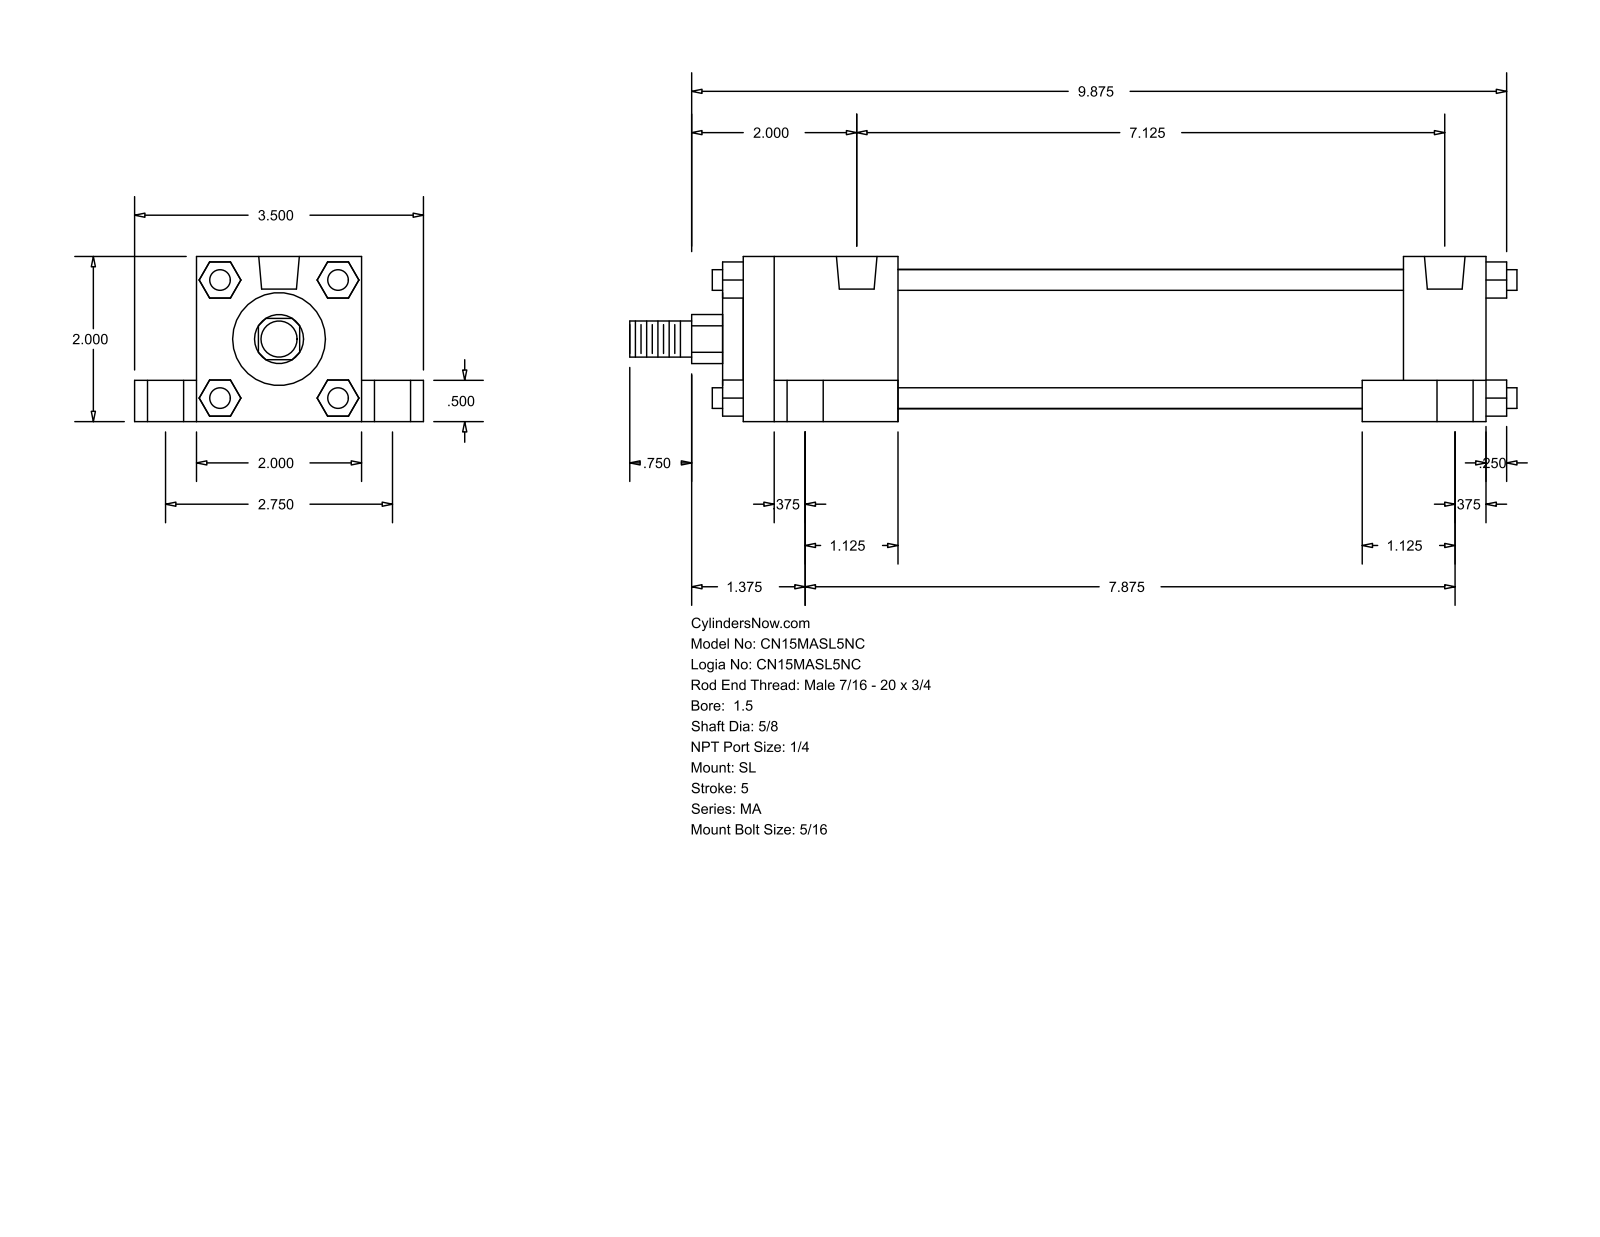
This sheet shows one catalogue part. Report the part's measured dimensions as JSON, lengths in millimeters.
{"part_name": "MA_SL__0150_0.625", "step_written_by": "GSSL Pune (CONFIG_CONTROL_DESIGN)", "units": "millimeters", "bodies": {"solids": 0, "faces": 148, "planar": 112, "cylindrical": 36, "other": 0}, "overall_size": [273.05, 88.9, 50.8], "round_holes": [[7.94, 4], [11.11, 4], [17.46, 4], [12.49, 2]], "round_bosses_or_shafts": [[6.35, 4], [42.93, 1], [28.57, 1], [15.88, 1], [11.11, 1]], "partial_cylinders_radius": [[7.54, 1]], "face_to_face_distances": [50.8, 19.05, 38.1, 69.85, 12.7, 228.59, 155.57, 25.4, 6.35, 9.52], "hole_center_spacings": [35.06, 38.36, 69.84, 180.98, 187.43, 199.93, 200.03, 211.87]}
